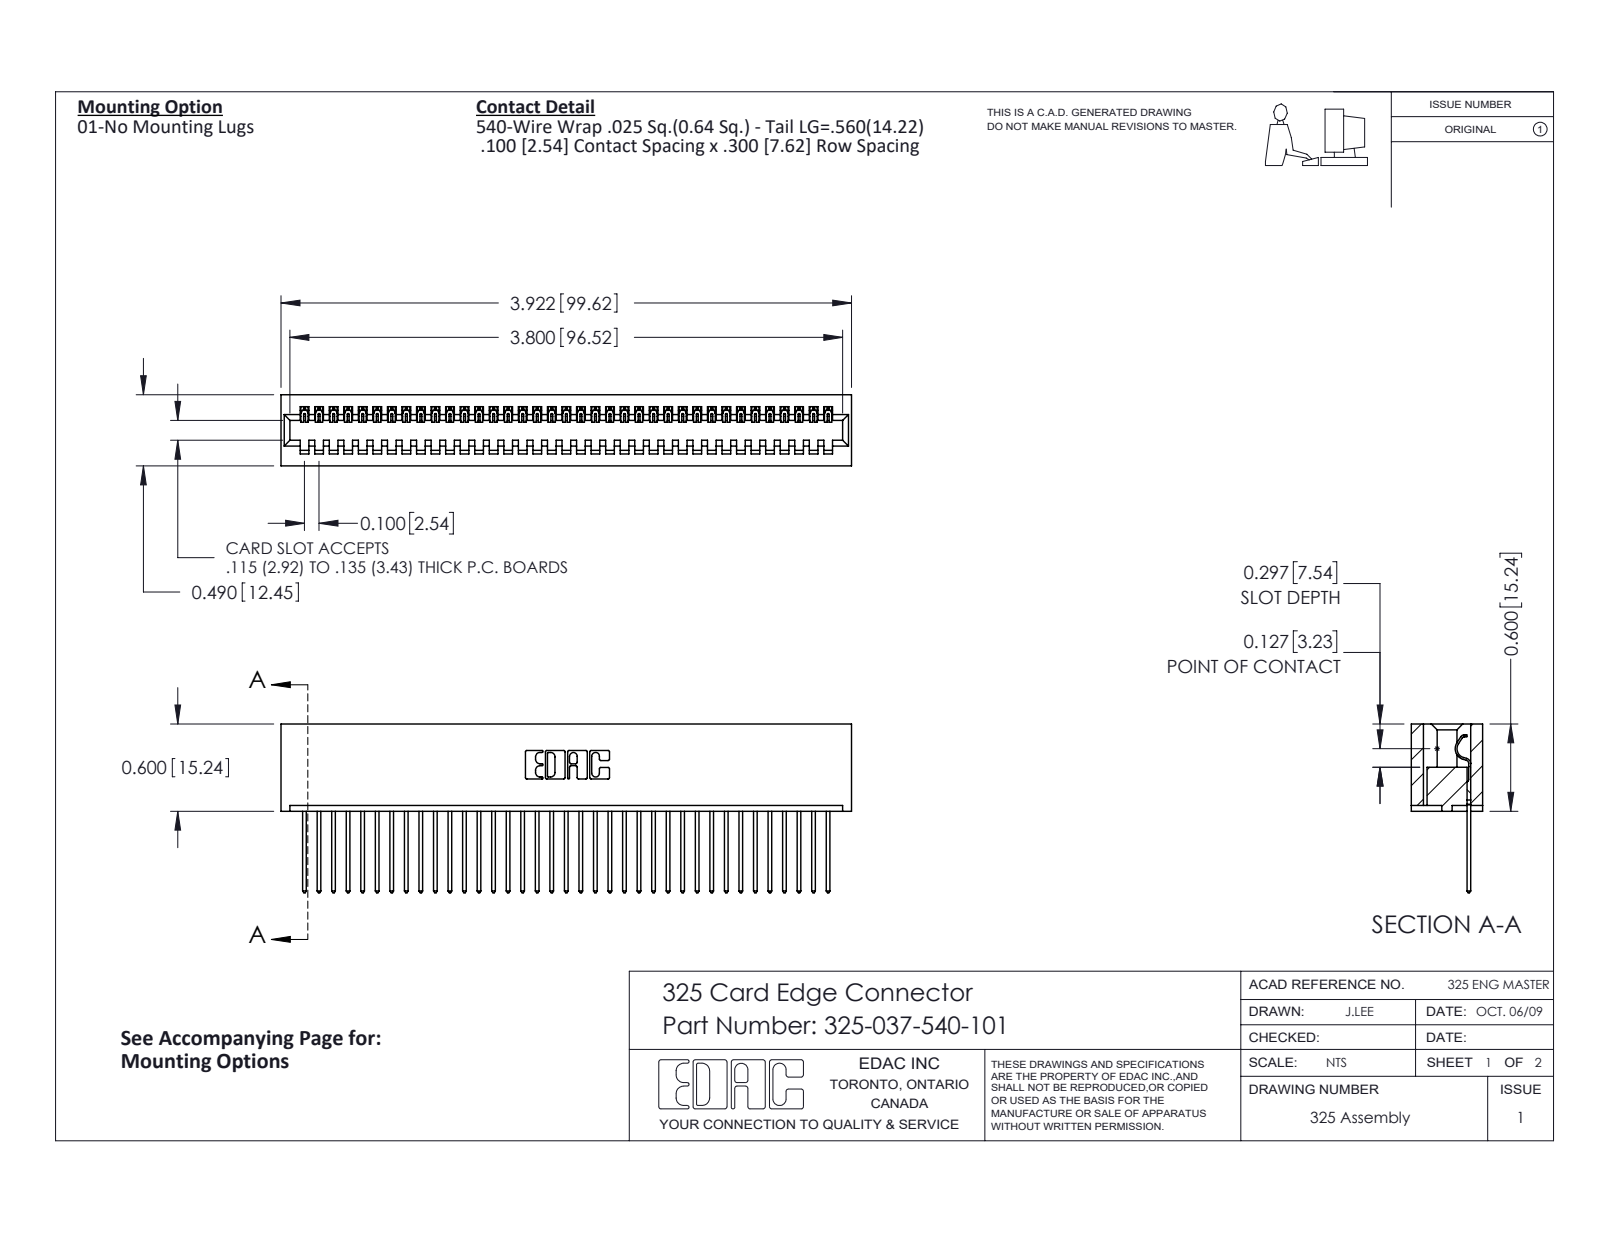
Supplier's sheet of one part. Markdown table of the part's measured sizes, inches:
| quantity | value |
| --- | --- |
| part name | 325-292-001_325-293-140; 325 Part_Lugless; 325-037-540-101 |
| STEP written by | SolidWorks 2016 (CONFIG_CONTROL_DESIGN) |
| units | inches |
| bodies | 38 solids, 2252 faces (1620 planar, 632 cylindrical, 0 other) |
| overall size | 3.922 × 1.16 × 0.49 |
| volume | 0.807 in³ |
| surface area | 23.61 in² |
| partial cylindrical surfaces (radius × count) | 0.006 × 74, 0.01 × 74, 0.01 × 22, 0.007 × 6, 0.031 × 6, 0.026 × 3, 0.014 × 1, 0.022 × 1 |
| main face-to-face distances | 0.083, 0.407, 0.3, 0.49, 0.107, 0.383, 0.025, 0.325, 0.56, 0.263 |
